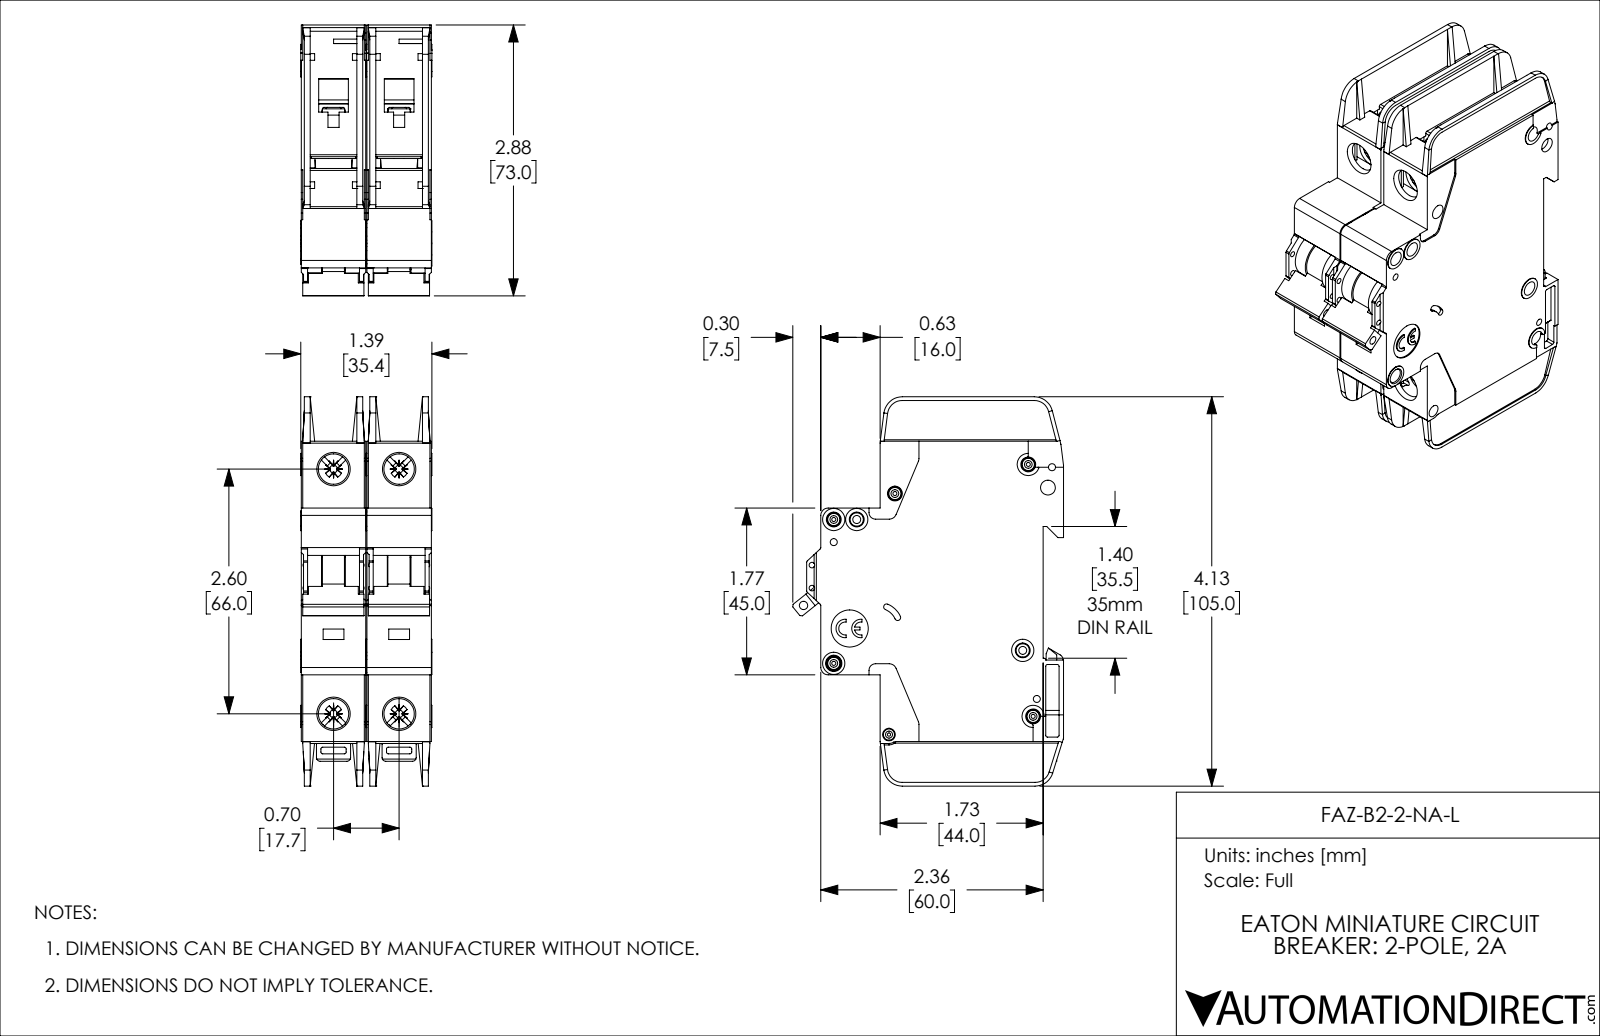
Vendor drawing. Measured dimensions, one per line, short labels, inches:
name: FAZ-B2-2-NA-L
written by: SolidWorks 2019 (AUTOMOTIVE_DESIGN)
unit: in
bodies: 2 solids, 2254 faces (1342 planar, 714 cylindrical, 198 other)
size: 4.134 × 2.876 × 1.394
volume: 9.365 in³; area: 82.01 in²
holes: 8× ⌀0.157, 5× ⌀0.043, 4× ⌀0.075, 4× ⌀0.323, 2× ⌀0.059, 2× ⌀0.085, 1× ⌀0.035, 1× ⌀0.089, 1× ⌀0.098, 1× ⌀0.134, 1× ⌀0.394
bosses: 5× ⌀0.13, 4× ⌀0.236, 3× ⌀0.118, 2× ⌀0.098
rounds: 57× R0.02, 20× R0.016, 14× R0.039, 10× R0.079, 8× R0.043, 5× R0.008, 5× R0.197, 4× R0.01
face distances: 0.697, 0.047, 0.685, 0.591, 0.094, 0.638, 0.543, 1.382, 0.744, 0.65
hole spacings: 0.244, 0.537, 0.697, 0.87, 2.598, 2.69, 0.189, 0.199
